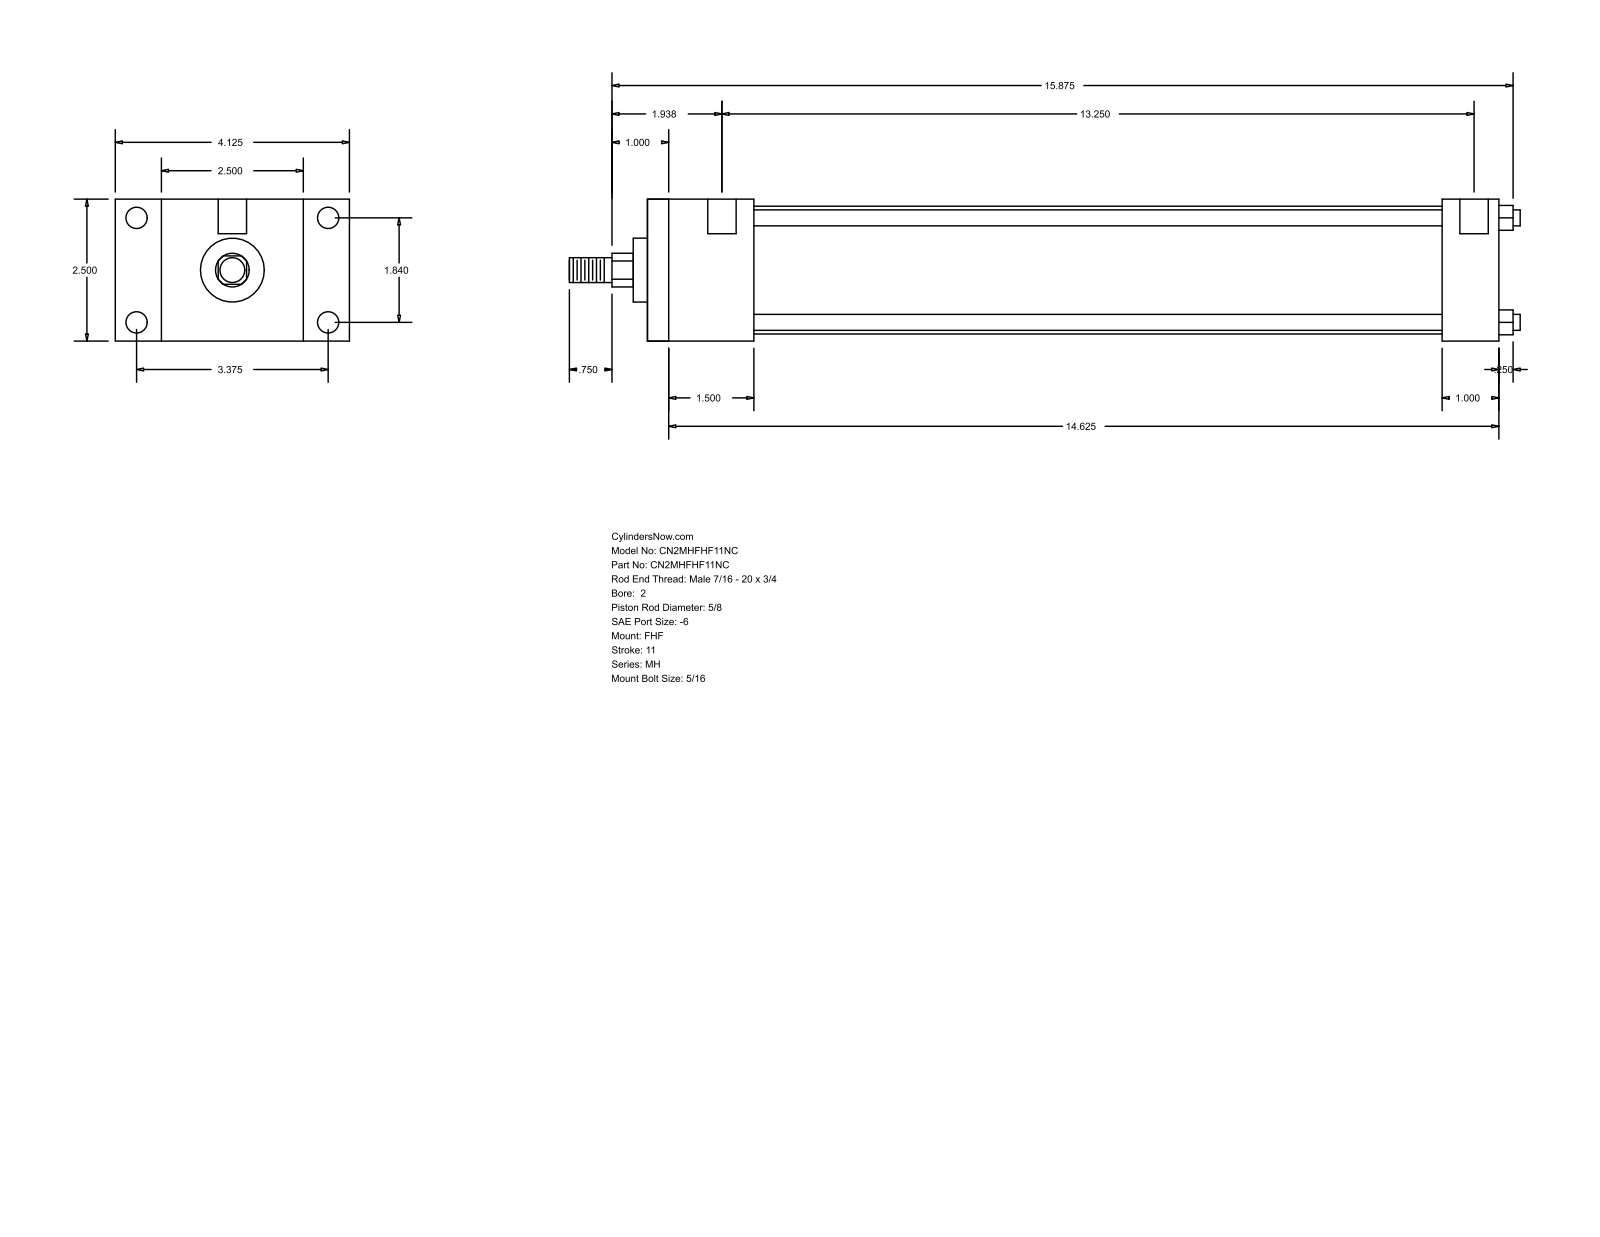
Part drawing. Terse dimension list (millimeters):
name: MH_FHF__0200_0.625
written by: GSSL Pune (CONFIG_CONTROL_DESIGN)
unit: mm
bodies: 0 solids, 88 faces (60 planar, 28 cylindrical, 0 other)
size: 425.45 × 104.78 × 63.5
holes: 4× ⌀5.56, 4× ⌀9.53, 2× ⌀12.7
bosses: 4× ⌀7.14, 1× ⌀57.15, 1× ⌀28.57, 1× ⌀15.88, 1× ⌀11.11
rounds: 1× R7.54
face distances: 63.5, 47.62, 381, 333.38, 20.64, 84.14, 104.78, 25.4, 355.6, 307.98
hole spacings: 46.74, 85.72, 97.63, 344.49, 3.18, 4.76, 336.55, 339.73
